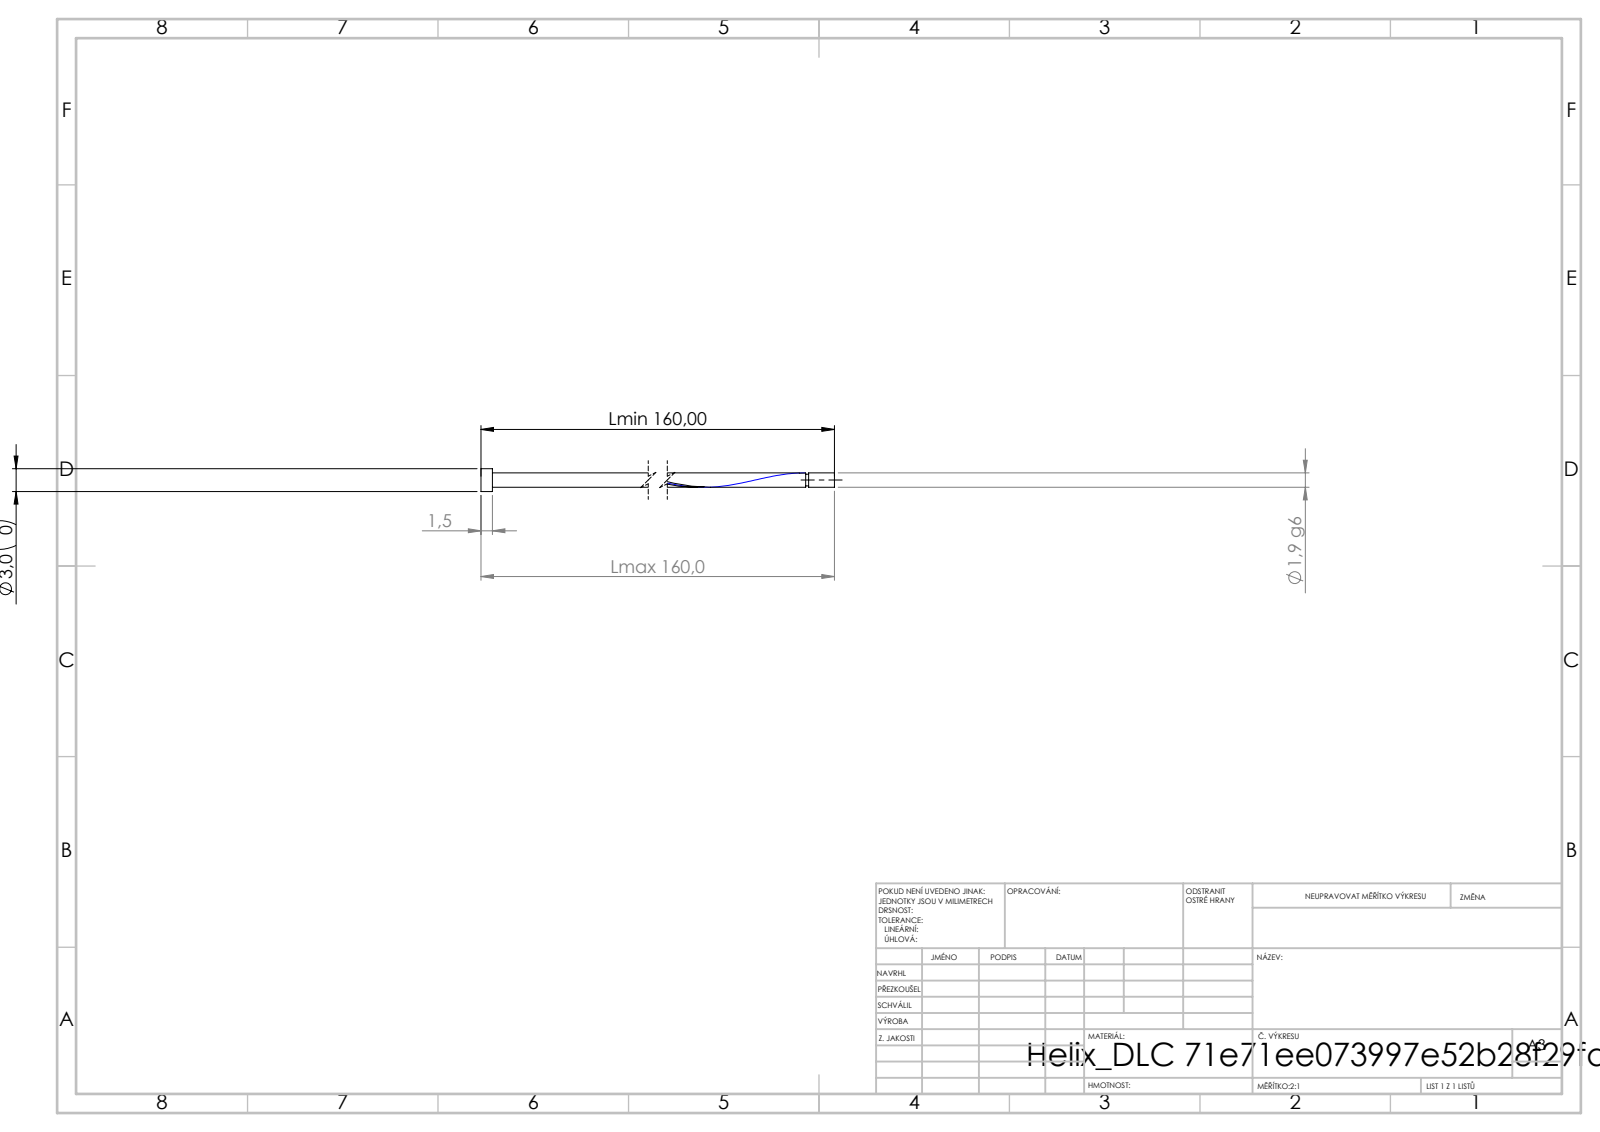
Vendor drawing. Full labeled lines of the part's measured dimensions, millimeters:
STEP written by: SolidWorks 2019 (CONFIG_CONTROL_DESIGN)
Units: millimetres
Bodies: 1 solid, 16 faces (6 planar, 9 cylindrical, 1 other)
Overall size (bounding box): 160 × 3 × 3
Volume: 556 mm³ · Surface area: 1 309 mm²
Round bosses / shafts (diameter × count): ⌀3 ×1, ⌀1.9 ×1, ⌀1.52 ×1
Main face-to-face distances: 1.5, 160, 158.5, 156.6, 155.1, 3.4, 156.22, 154.72, 0.38, 3.78
